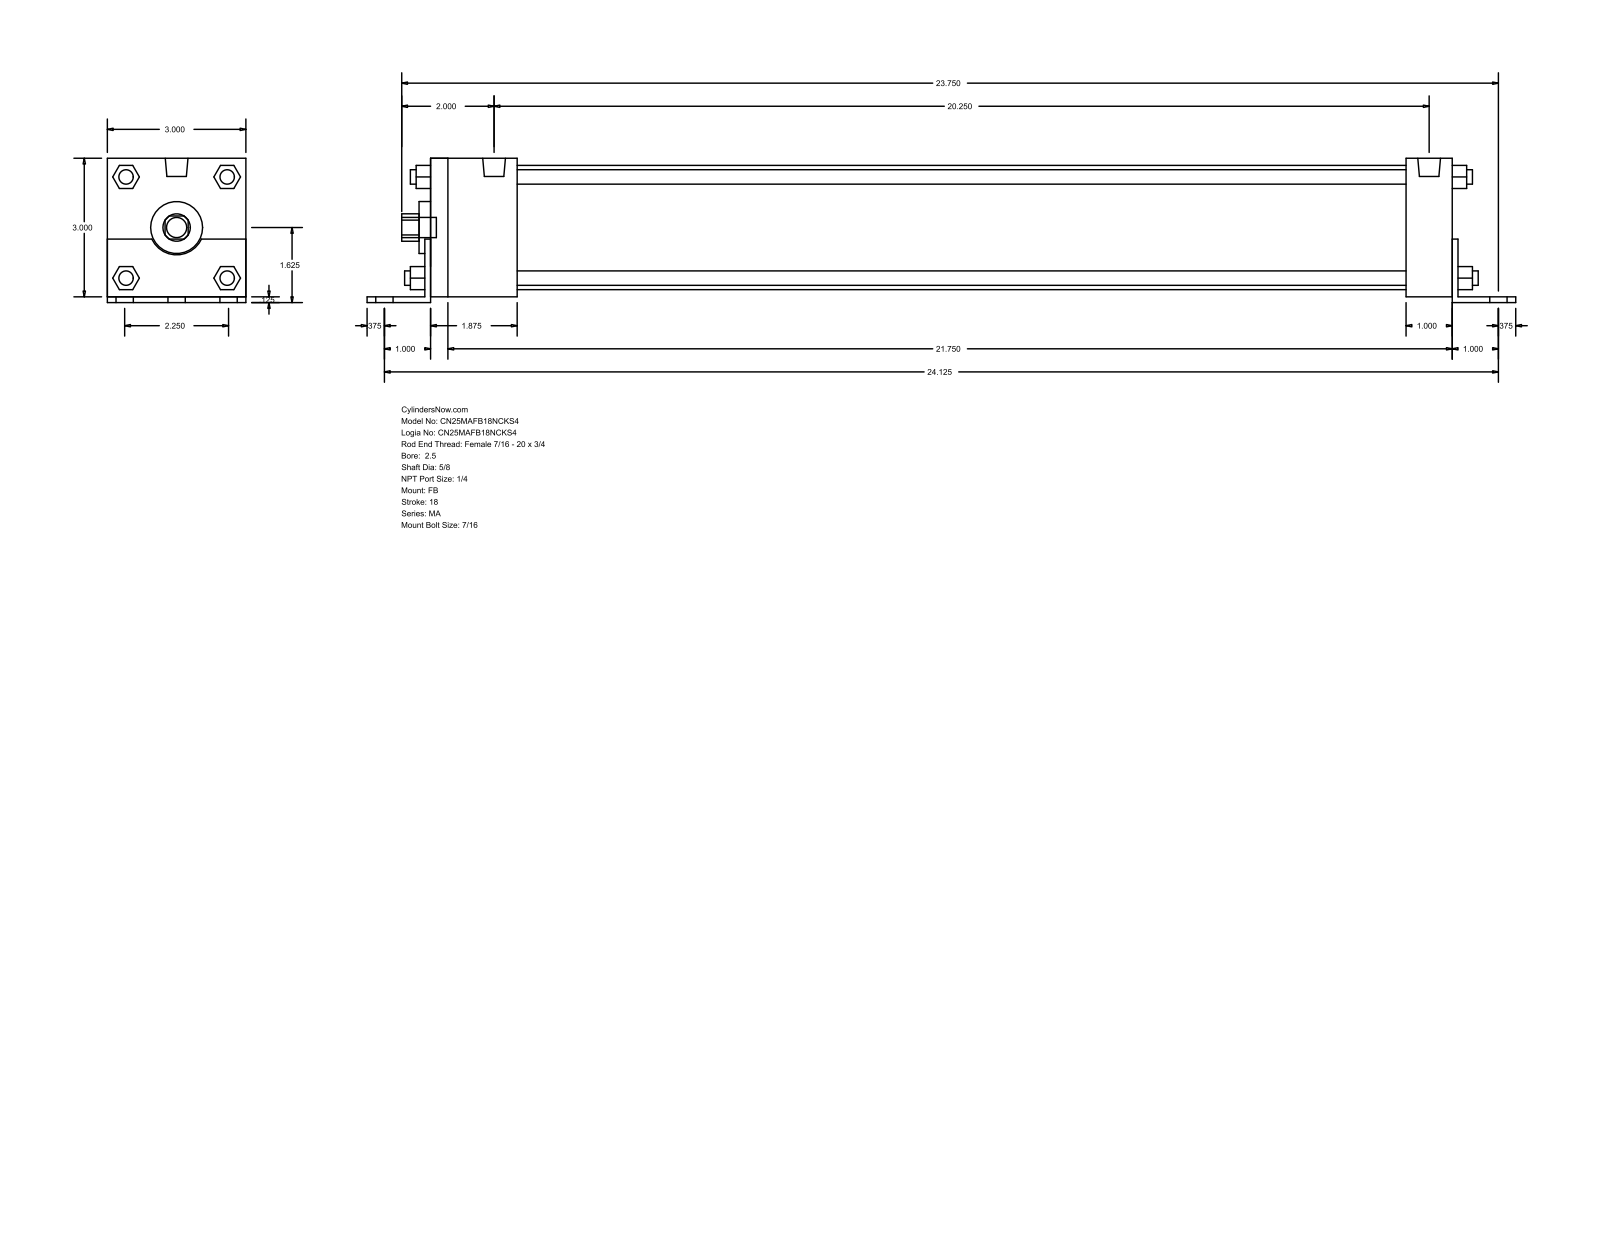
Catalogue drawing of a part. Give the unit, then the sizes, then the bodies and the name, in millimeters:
Units: millimetres
Overall size (bounding box): 631.83 × 79.38 × 76.2
Round holes (diameter × count): ⌀15.88 ×1, ⌀28.57 ×1, ⌀68.33 ×1
Round bosses / shafts (diameter × count): ⌀7.94 ×8, ⌀11.11 ×7, ⌀12.49 ×2
Partial cylindrical surfaces — rounded edges, fillets, slot ends (radius × count): R7.54 ×1, R15.05 ×1
Main face-to-face distances: 76.2, 3.17, 79.37, 561.97, 568.32, 3.18, 565.14, 47.62, 25.4, 565.15
Bodies: 0 solids, 140 faces (105 planar, 35 cylindrical, 0 other)
Part name (STEP PRODUCT): MA_FB__0250_0.625
STEP written by: GSSL Pune (CONFIG_CONTROL_DESIGN)
